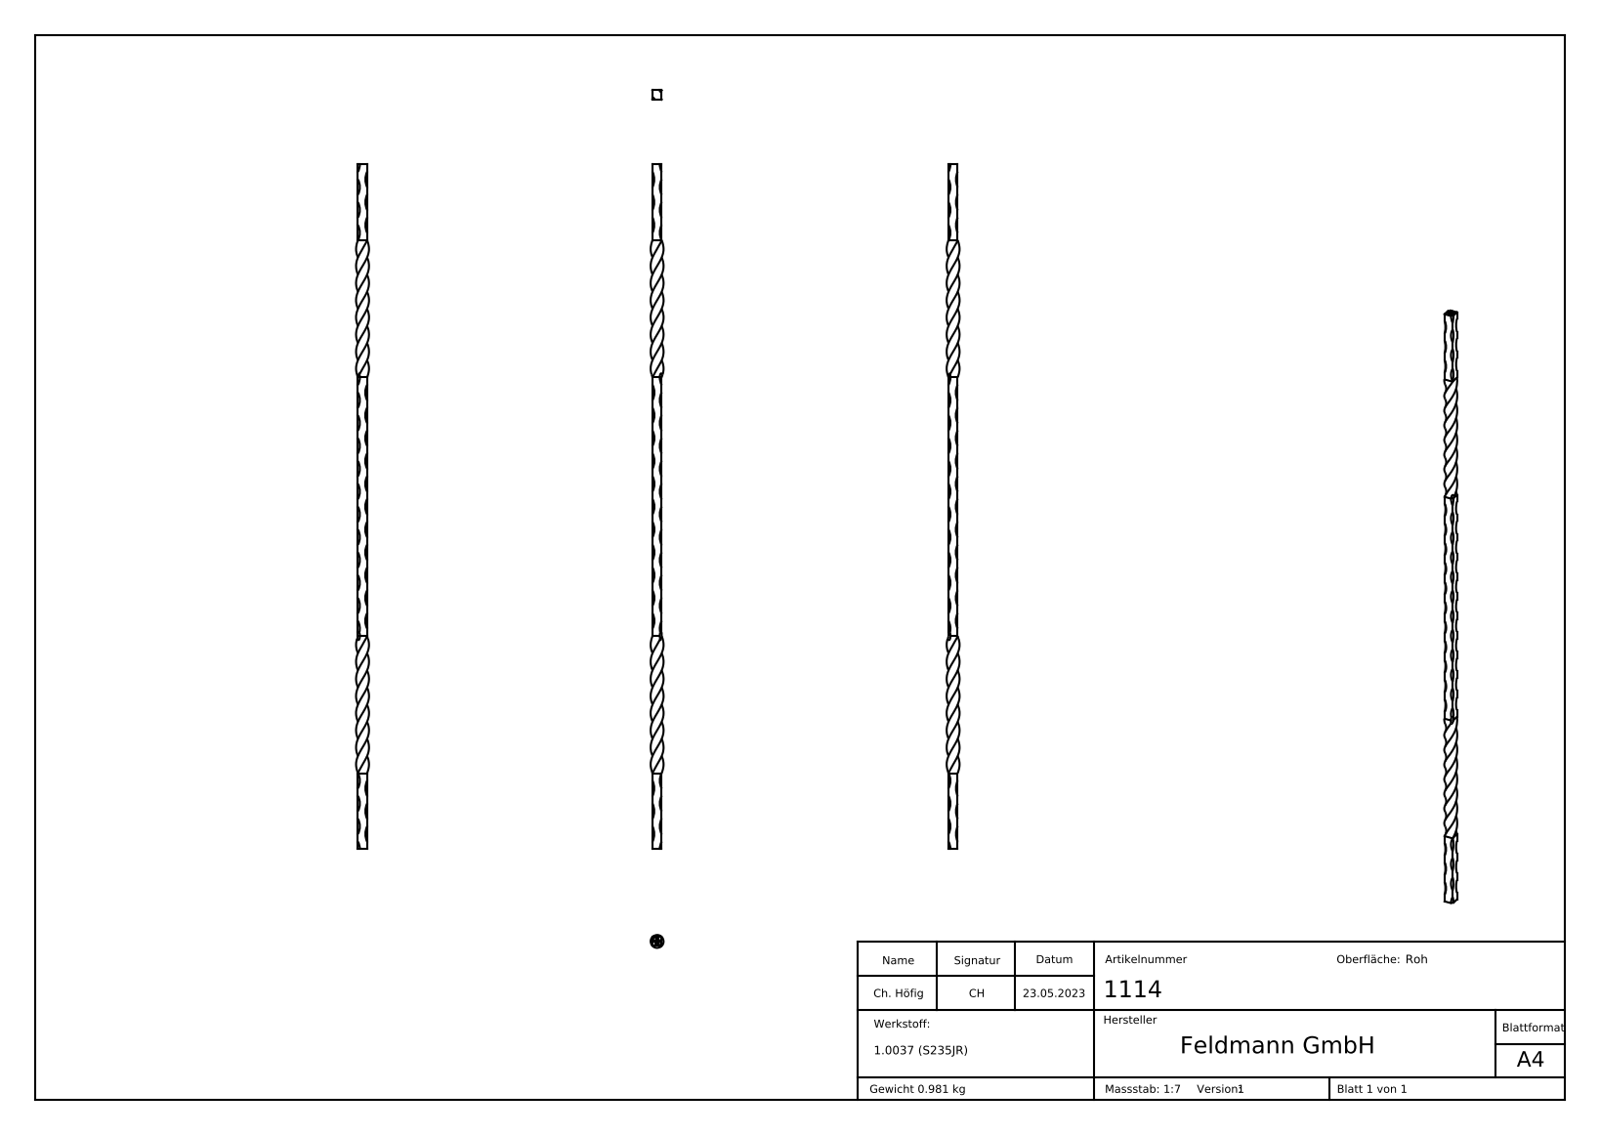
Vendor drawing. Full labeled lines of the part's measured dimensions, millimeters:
Part name (STEP PRODUCT): 1114
STEP written by: SolidWorks 2018 (CONFIG_CONTROL_DESIGN)
Units: millimetres
Bodies: 1 solid, 292 faces (138 planar, 0 cylindrical, 154 other)
Overall size (bounding box): 900 × 17.03 × 17.03
Volume: 125 745 mm³ · Surface area: 43 011 mm²
Main face-to-face distances: 12, 900, 899.9, 1.02, 0.57, 1.14, 2.7, 1.25, 1.59, 0.45
